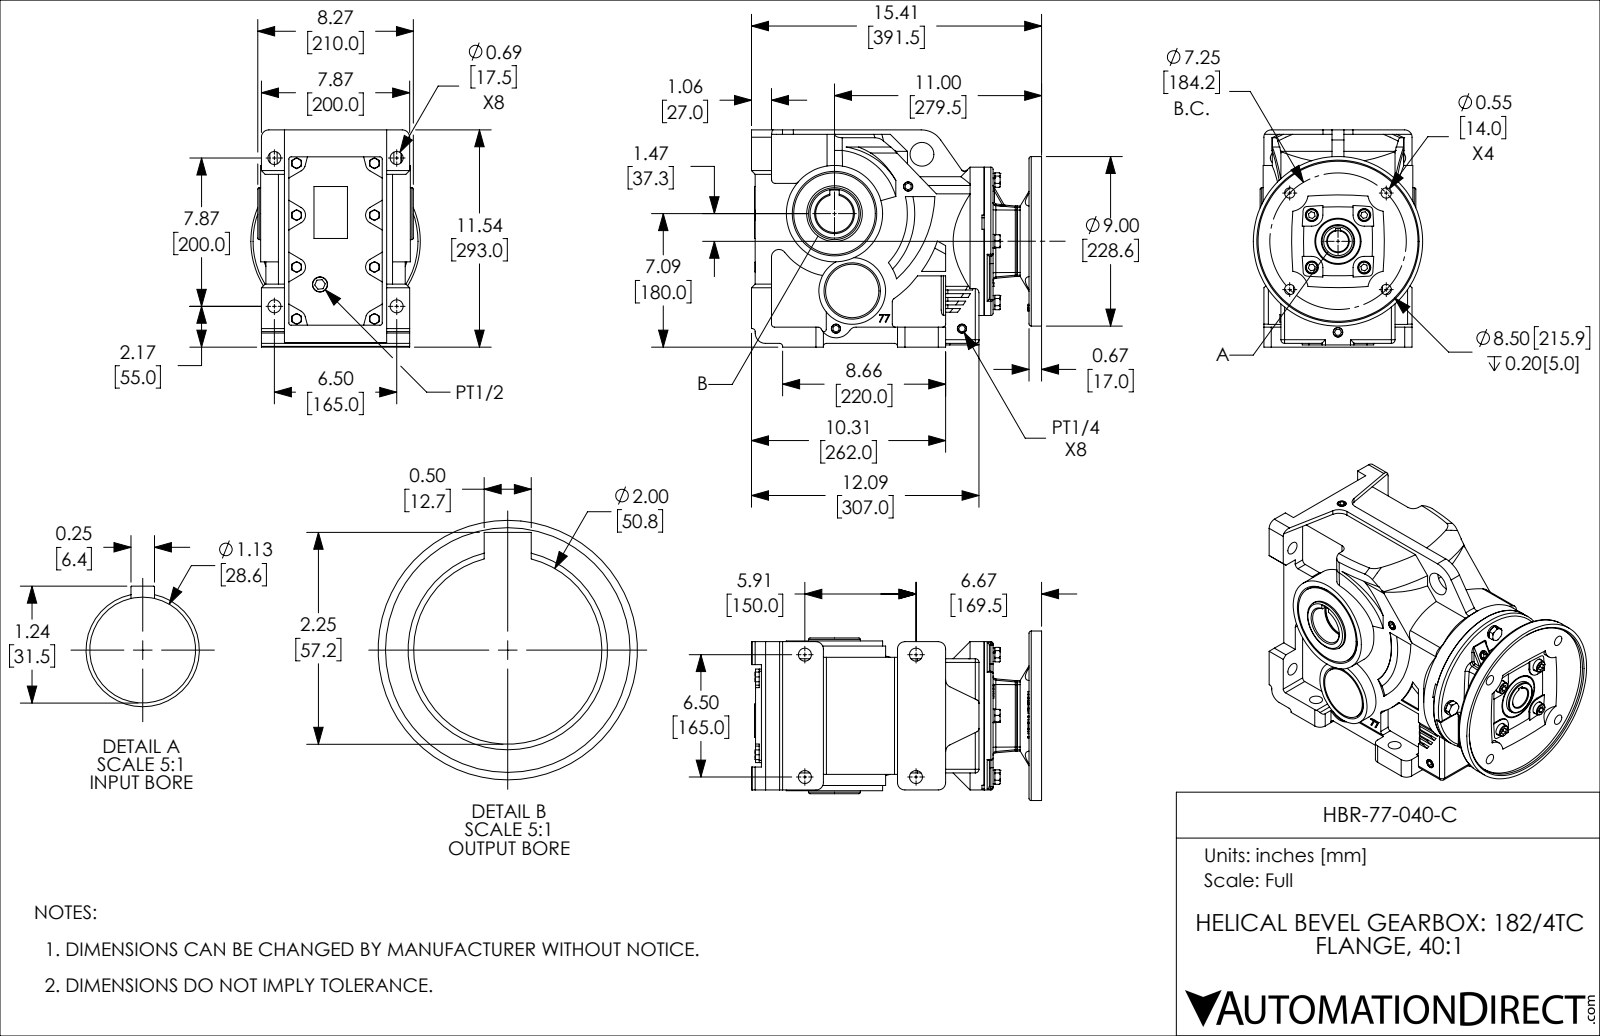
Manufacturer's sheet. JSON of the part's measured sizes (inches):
{"part_name": "HBR-77-040-C", "step_written_by": "SolidWorks 2018 (AUTOMOTIVE_DESIGN)", "units": "inches", "bodies": {"solids": 43, "faces": 1761, "planar": 783, "cylindrical": 582, "other": 396}, "overall_size": [15.413, 11.535, 9], "volume_in3": 339.1, "surface_area_in2": 1869, "round_holes": [[0.689, 12], [0.268, 8], [0.335, 8], [0.354, 8], [0.433, 8], [0.394, 4], [0.402, 4], [0.551, 4], [0.438, 3], [0.118, 2], [0.487, 2], [2.165, 2]], "round_bosses_or_shafts": [[0.315, 8], [0.63, 5], [0.724, 4], [0.394, 4], [9, 1], [7.874, 1], [5.118, 1], [3.543, 1]], "partial_cylinders_radius": [[0.394, 36], [0.118, 14], [0.197, 12], [0.315, 12], [0.157, 11], [0.472, 10], [0.591, 7], [0.079, 5]], "face_to_face_distances": [0.236, 0.472, 0.315, 4.961, 0.276, 5.748, 0.787, 5.276, 0.512, 0.551], "hole_center_spacings": [2.653, 2.756, 4.844, 4.968, 6.352, 6.496, 1.656, 2.32]}
